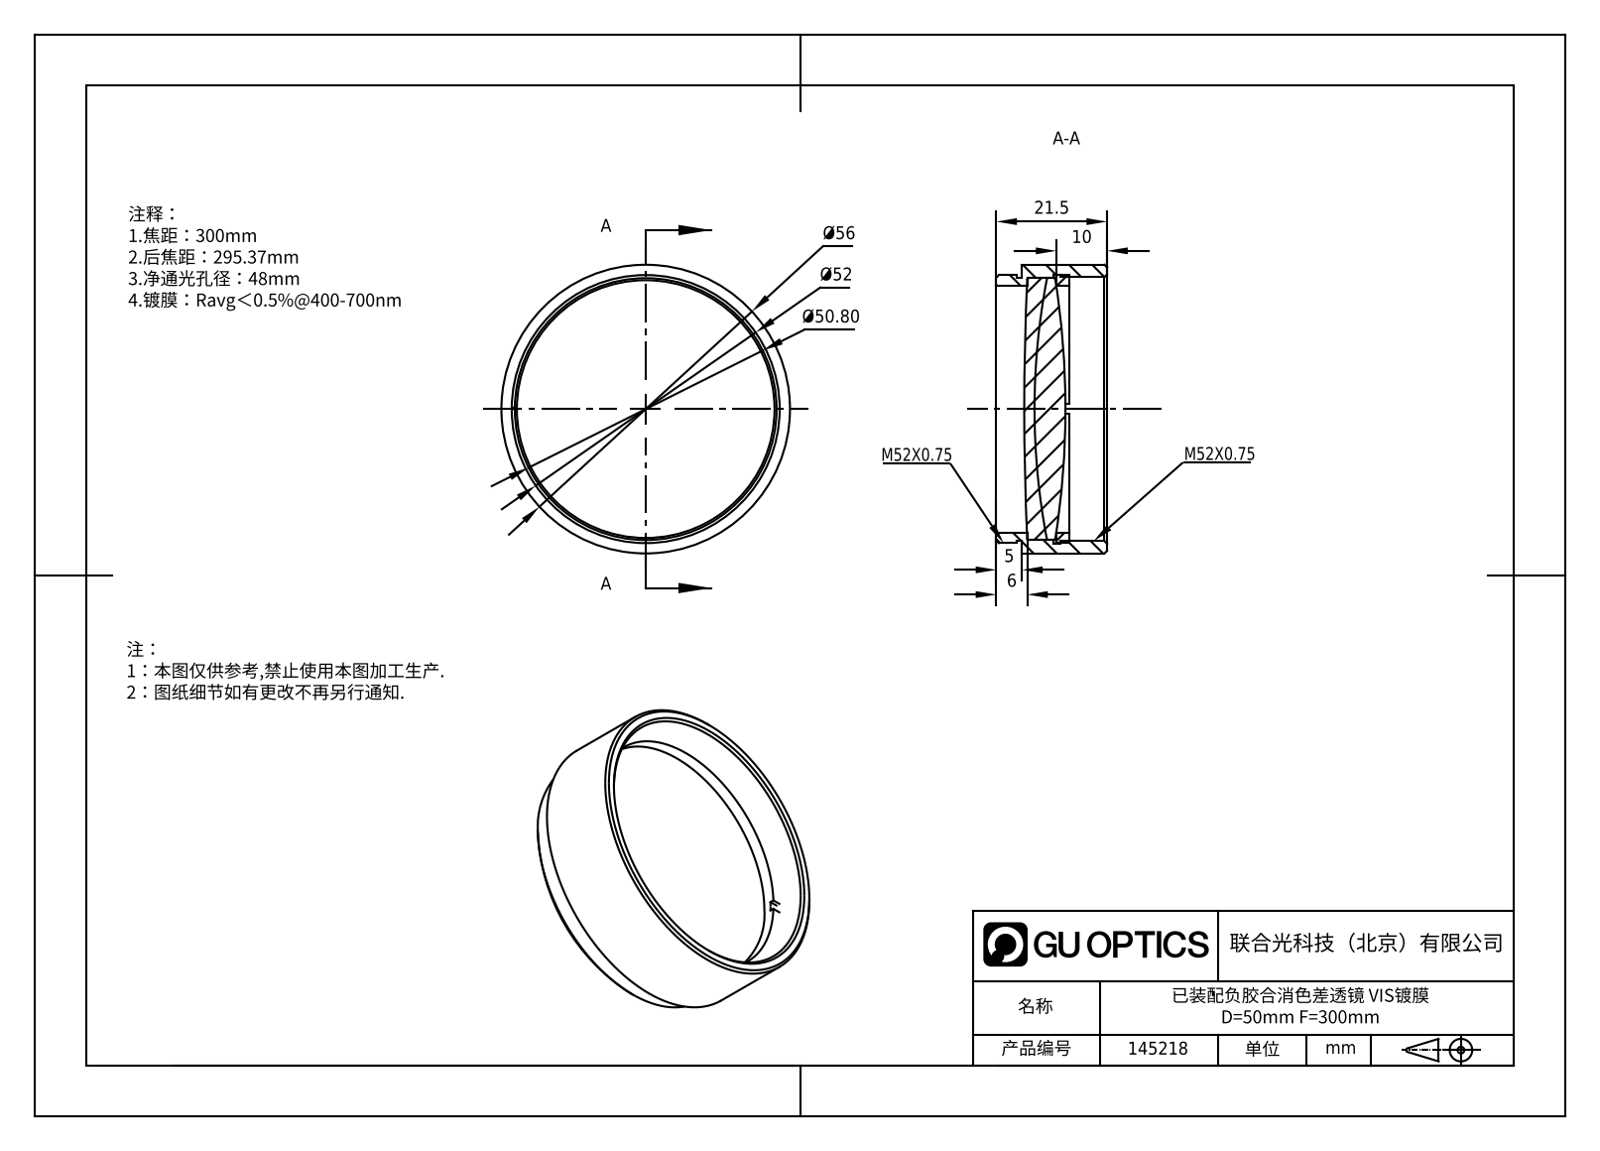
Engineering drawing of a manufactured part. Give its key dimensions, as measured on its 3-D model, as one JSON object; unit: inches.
{"part_name": "APD-ML50-300-VIS; M52x0.75安装环-PN35002-LM508-D1; GL31-050B-300-VIS_Solidworks; M52x0.75ѹȦ", "step_written_by": "SolidWorks 2022 (AUTOMOTIVE_DESIGN)", "units": "inches", "bodies": {"solids": 4, "faces": 58, "planar": 16, "cylindrical": 22, "other": 20}, "overall_size": [2.205, 2.205, 0.846], "volume_in3": 1.385, "surface_area_in2": 29.38, "round_holes": [[1.89, 1], [2.018, 1], [2.051, 1]], "round_bosses_or_shafts": [[2.205, 1], [2.047, 1], [2.008, 1], [2, 1]], "face_to_face_distances": [0.197, 0.236, 0.359, 0.039, 0.261, 0.098, 0.458, 0.556, 0.846, 0.65]}
